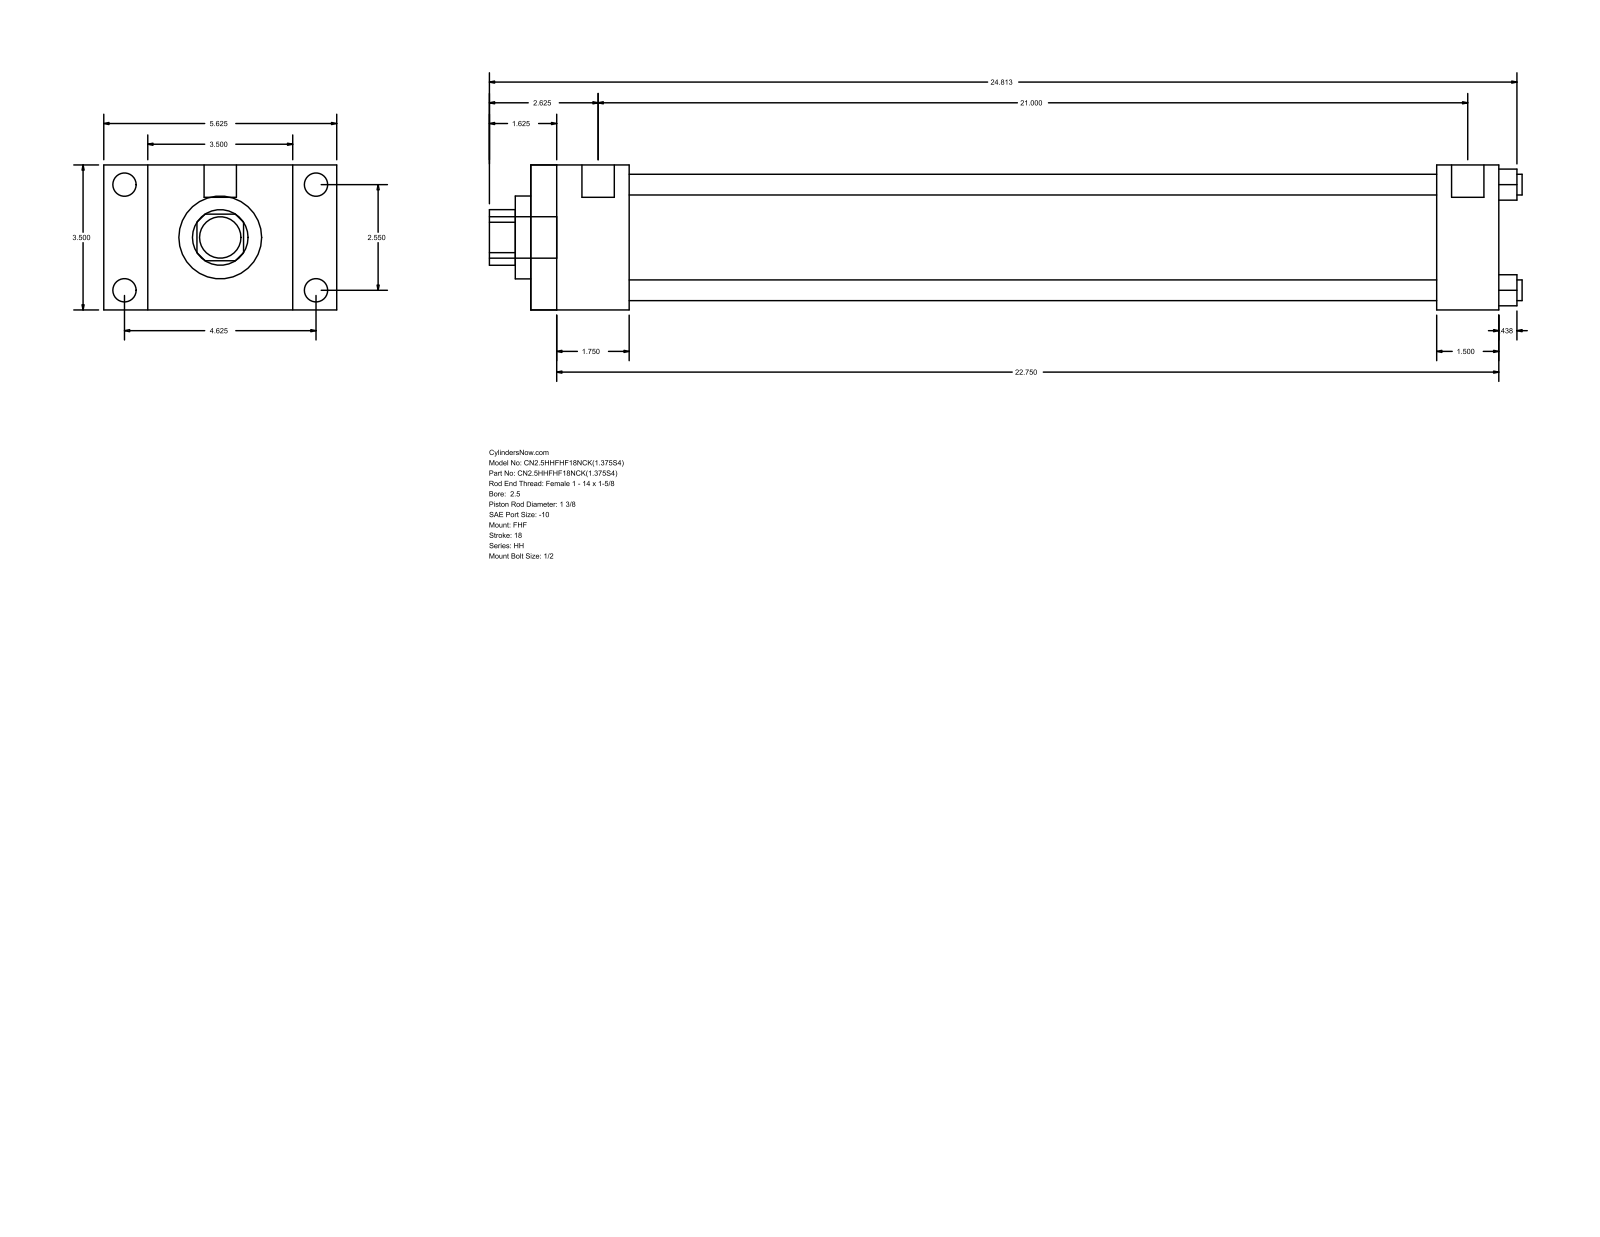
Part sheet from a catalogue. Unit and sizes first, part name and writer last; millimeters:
Units: millimetres
Overall size (bounding box): 633.41 × 142.88 × 88.9
Round holes (diameter × count): ⌀12.7 ×4, ⌀34.92 ×1, ⌀50.8 ×1, ⌀73.03 ×1
Round bosses / shafts (diameter × count): ⌀14.3 ×4, ⌀5.56 ×4, ⌀19.84 ×2, ⌀25.4 ×1
Partial cylindrical surfaces — rounded edges, fillets, slot ends (radius × count): R17.06 ×1
Main face-to-face distances: 88.9, 60.32, 26.99, 115.89, 593.72, 533.4, 142.88, 555.62, 495.3, 38.1
Hole centre spacings: 45.79, 64.76, 91.58
Bodies: 0 solids, 88 faces (60 planar, 28 cylindrical, 0 other)
Part name (STEP PRODUCT): HH_FHF__0250_1.375
STEP written by: GSSL Pune (CONFIG_CONTROL_DESIGN)
